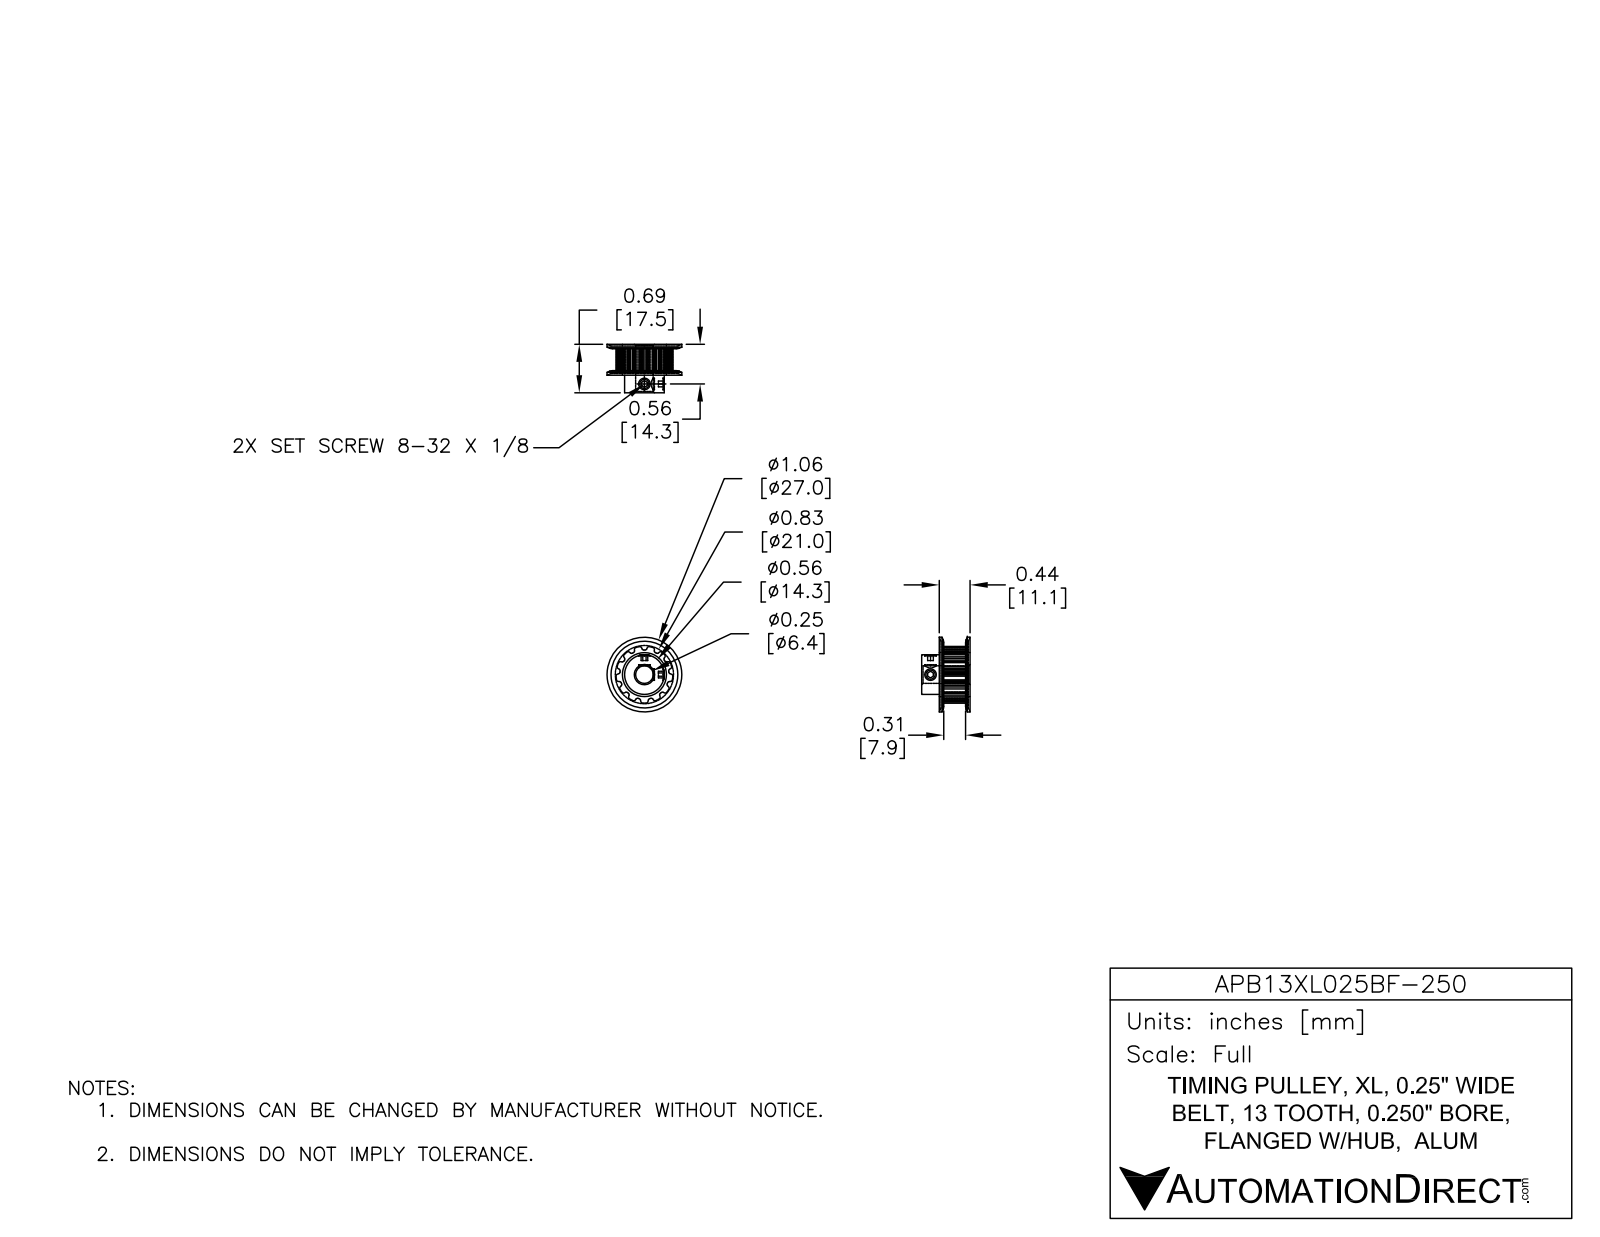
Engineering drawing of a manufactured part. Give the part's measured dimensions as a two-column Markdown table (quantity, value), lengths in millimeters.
| quantity | value |
| --- | --- |
| part name | APB13XL025BF-250 |
| STEP written by | SolidWorks 2014 (AUTOMOTIVE_DESIGN) |
| units | millimeters |
| bodies | 1 solid, 155 faces (45 planar, 88 cylindrical, 22 other) |
| overall size | 27 × 27 × 17.5 |
| volume | 3 970 mm³ |
| surface area | 3 152 mm² |
| round holes (diameter × count) | 2.2 × 2, 6.4 × 1 |
| round bosses / shafts (diameter × count) | 14.3 × 1 |
| partial cylindrical surfaces (radius × count) | 0.4 × 52, 8.9 × 1 |
| main face-to-face distances | 9.5, 0.8, 10.3, 17.5, 16.7, 7.1, 0.8, 8.7, 1.7, 15.8 |
